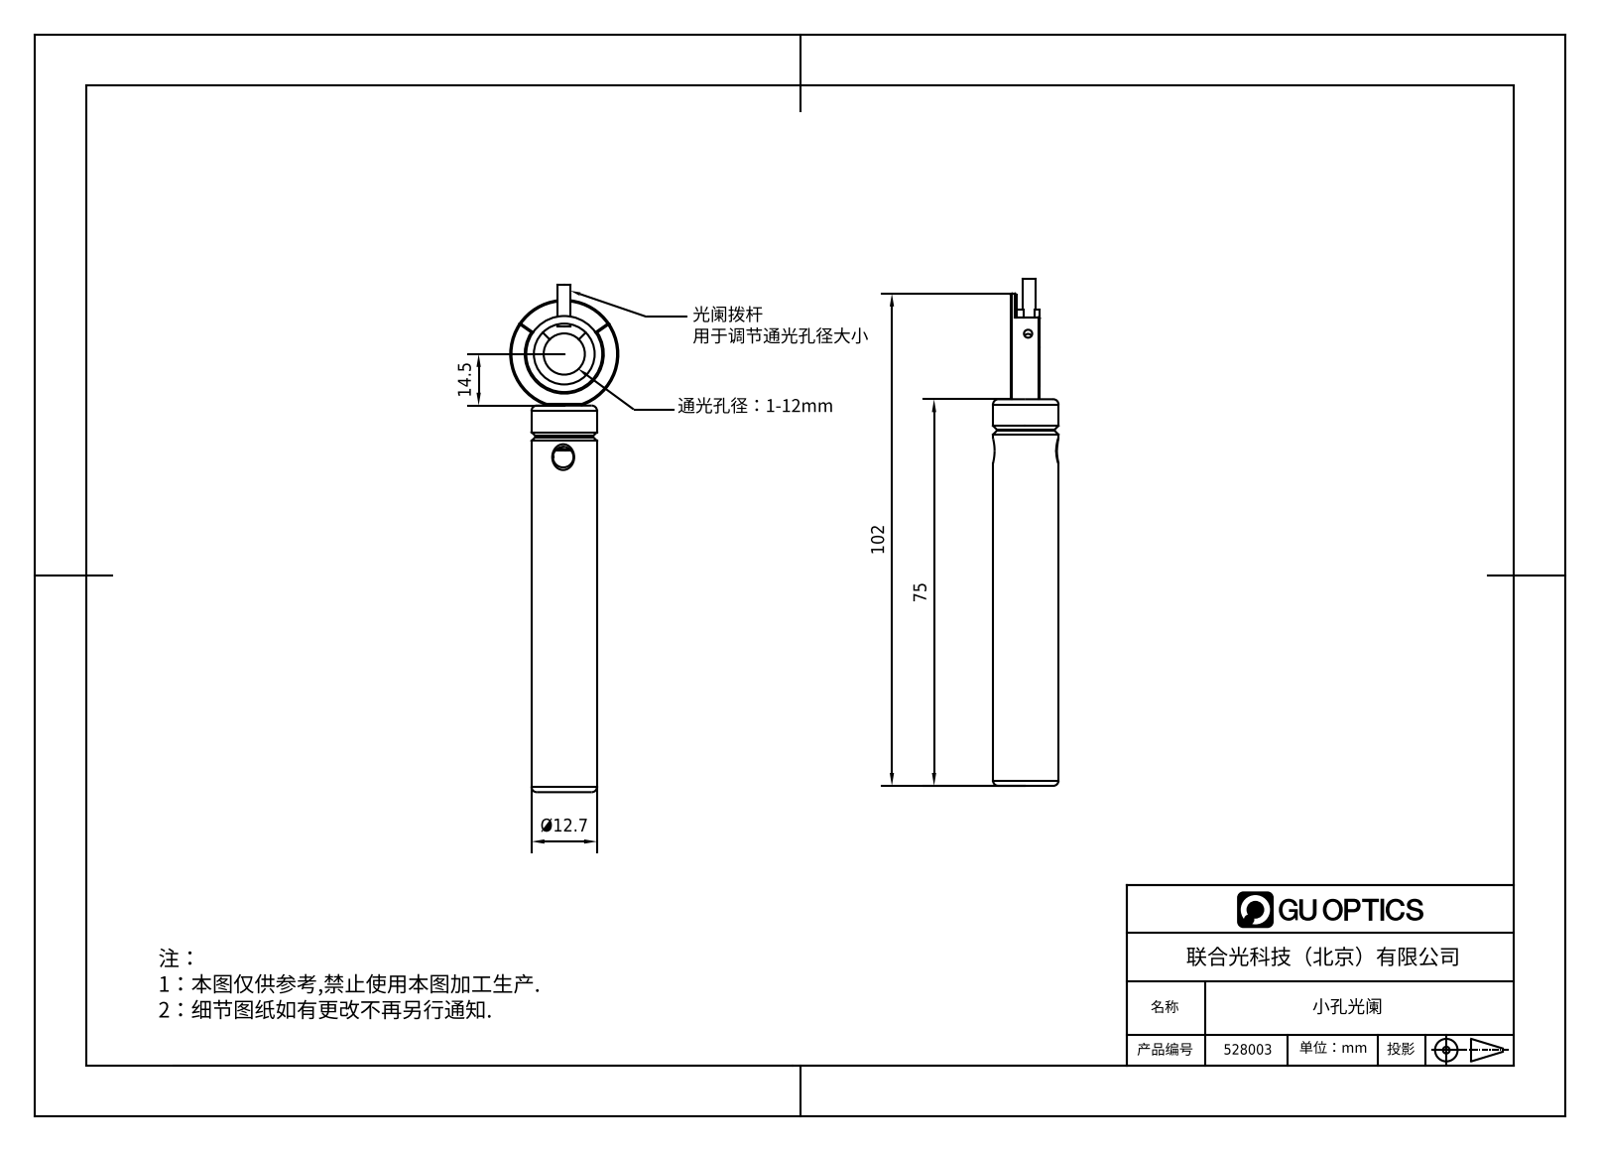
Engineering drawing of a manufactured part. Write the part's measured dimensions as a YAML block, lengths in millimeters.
part_name: "528003"
step_written_by: "SolidWorks 2020 (CONFIG_CONTROL_DESIGN)"
units: millimeters
bodies: {solids: 0, faces: 230, planar: 100, cylindrical: 66, other: 64}
overall_size: [109.88, 27, 12.7]
round_holes:
  - {diameter: 1.5, count: 12}
  - {diameter: 1.6, count: 2}
  - {diameter: 1.25, count: 1}
  - {diameter: 3.3, count: 1}
  - {diameter: 4, count: 1}
  - {diameter: 5, count: 1}
  - {diameter: 12, count: 1}
  - {diameter: 13, count: 1}
  - {diameter: 17.5, count: 1}
  - {diameter: 19.75, count: 1}
round_bosses_or_shafts:
  - {diameter: 1.5, count: 8}
  - {diameter: 2, count: 2}
  - {diameter: 27, count: 1}
  - {diameter: 18.5, count: 1}
  - {diameter: 12.7, count: 1}
  - {diameter: 4, count: 1}
  - {diameter: 2.4, count: 1}
  - {diameter: 1.6, count: 1}
partial_cylinders:
  - {radius: 6.38, count: 10}
  - {radius: 0.75, count: 2}
  - {radius: 1.2, count: 2}
  - {radius: 1.5, count: 2}
  - {radius: 5.75, count: 1}
  - {radius: 8.75, count: 1}
  - {radius: 10, count: 1}
face_to_face_distances: [6.7, 6.55, 2.7, 4, 3.85, 1, 0.41, 4.26, 6.96, 5]
hole_center_spacings: [14.34, 10.62, 12.59, 13.12, 4.33, 4.6, 6.04, 7]
